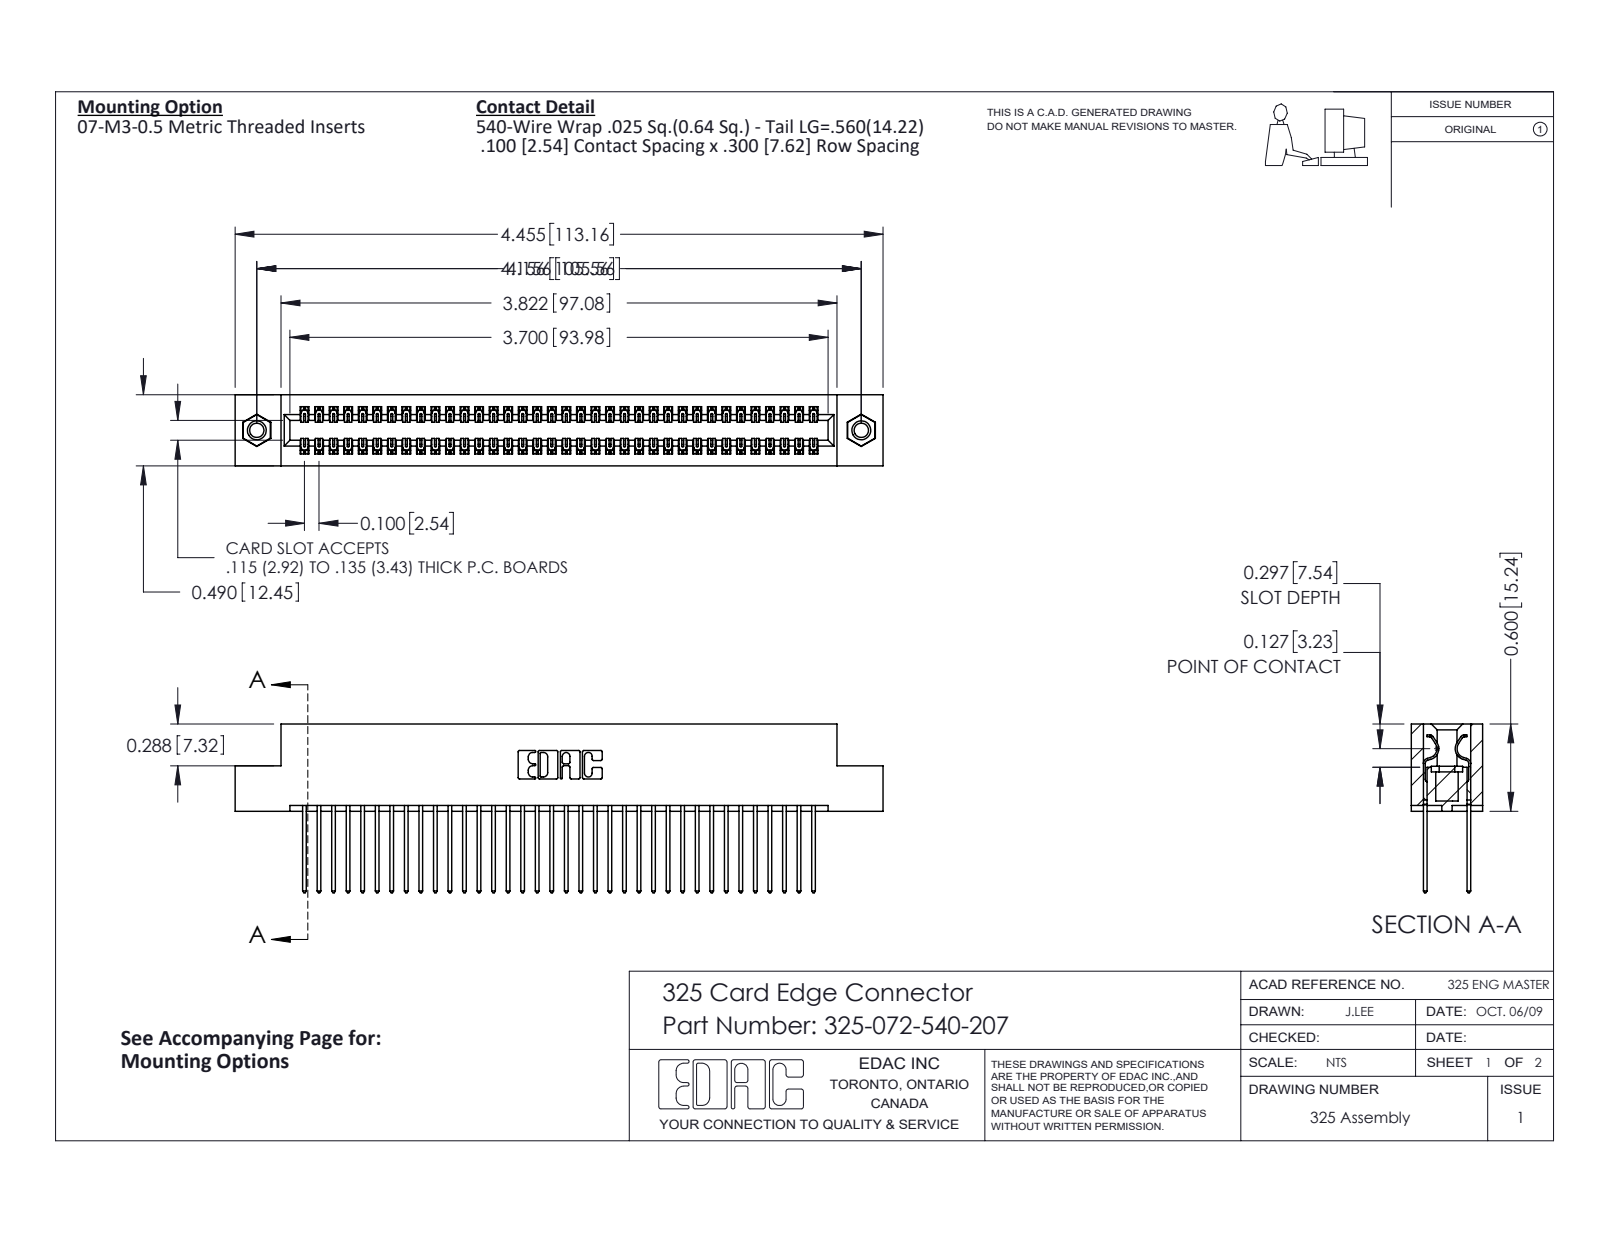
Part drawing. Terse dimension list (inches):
name: 345-250-001_345-250-005-103; 325-072-540-207; 325 Part_TI; 325-292-001_325-293-140
written by: SolidWorks 2016 (CONFIG_CONTROL_DESIGN)
unit: in
bodies: 75 solids, 3918 faces (2694 planar, 1208 cylindrical, 16 other)
size: 4.455 × 1.16 × 0.49
volume: 0.904 in³; area: 29.63 in²
holes: 2× ⌀0.098, 2× ⌀0.125, 2× ⌀0.16
bosses: 2× ⌀0.155
rounds: 108× R0.006, 72× R0.01, 22× R0.01, 6× R0.007, 6× R0.031, 3× R0.026, 2× R0.014, 2× R0.022
face distances: 0.083, 0.407, 0.3, 0.107, 0.383, 0.025, 0.49, 0.325, 0.275, 0.56
hole spacings: 4.156
